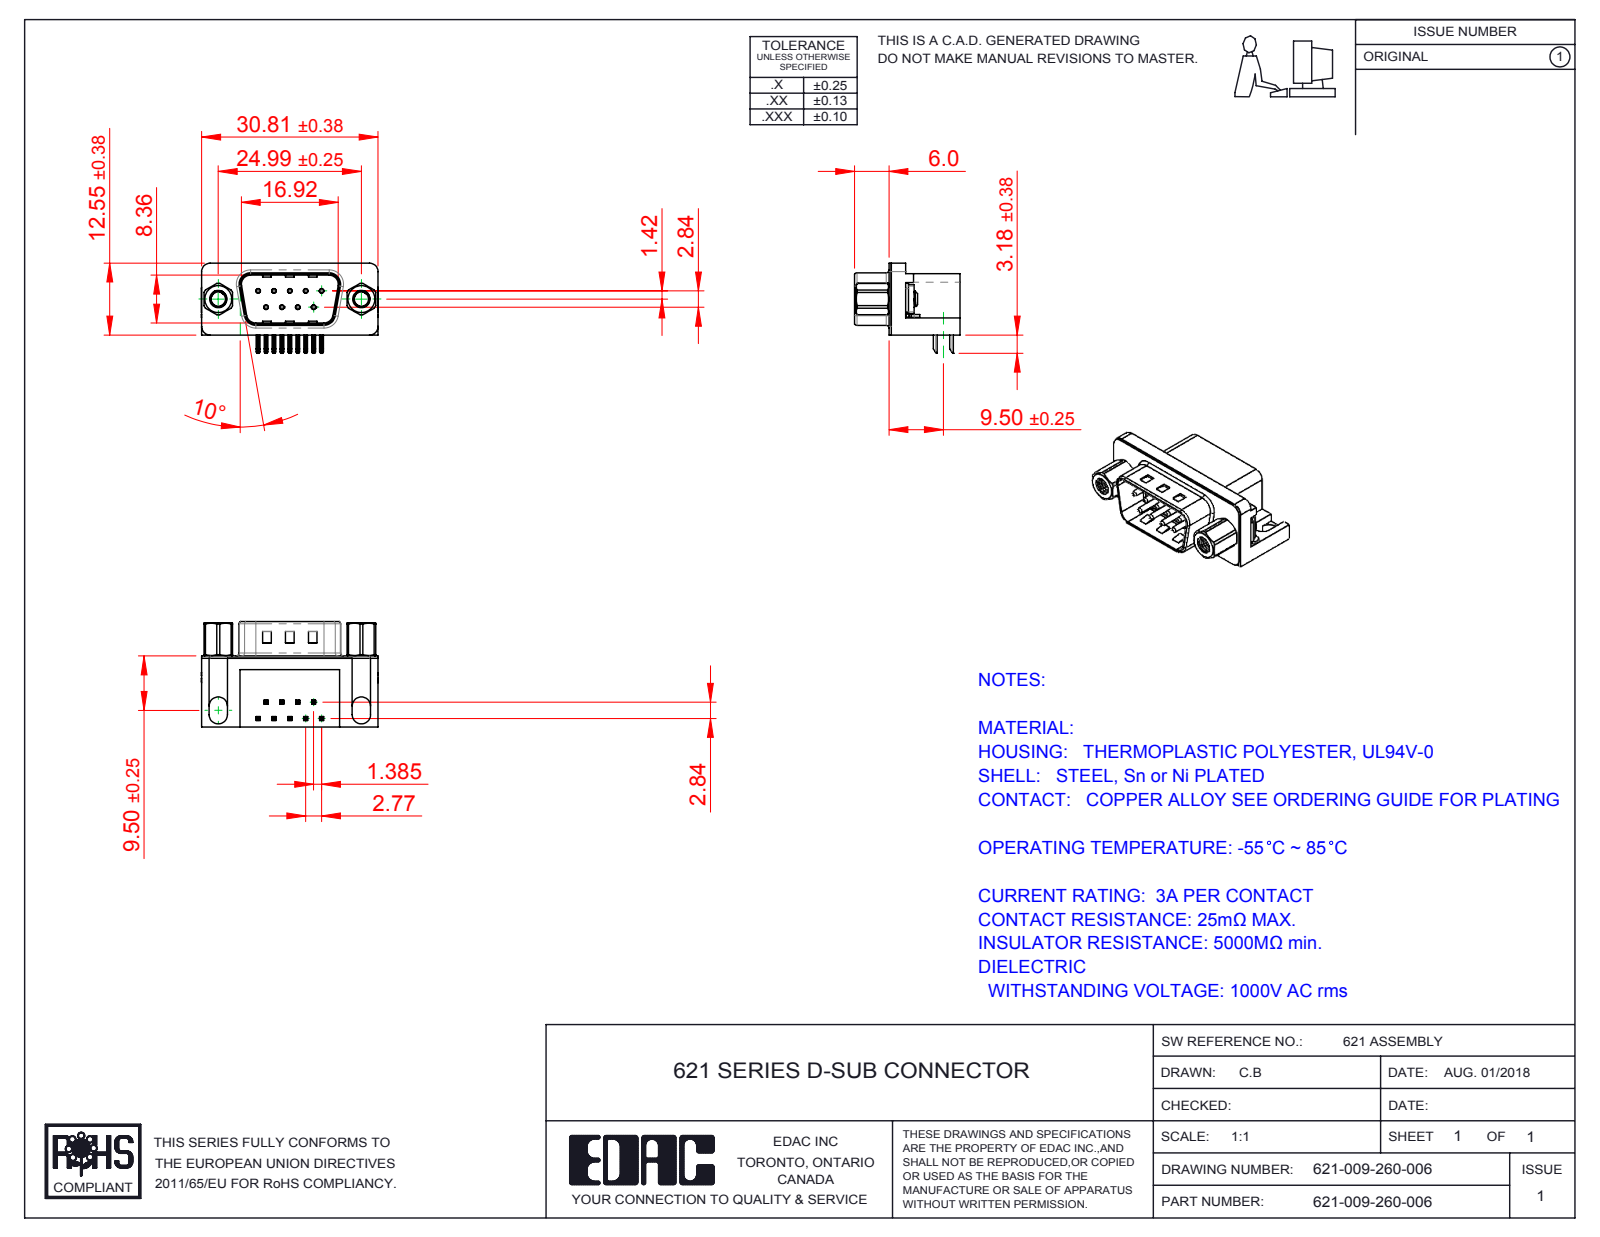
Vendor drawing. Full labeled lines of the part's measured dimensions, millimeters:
Part name (STEP PRODUCT): 621 Non Board Mount; 621 Contact Top; 621 Contact Bottom; 621 Shell_9 Socket (+4 more)
STEP written by: SolidWorks 2016 (CONFIG_CONTROL_DESIGN)
Units: millimetres
Bodies: 17 solids, 1133 faces (593 planar, 407 cylindrical, 133 other)
Overall size (bounding box): 30.89 × 18.4 × 15.73
Volume: 3 449 mm³ · Surface area: 4 780 mm²
Round holes (diameter × count): ⌀0.35 ×9, ⌀0.8 ×9, ⌀2.5 ×2, ⌀4 ×2, ⌀4.8 ×2, ⌀5 ×2
Round bosses / shafts (diameter × count): ⌀0.75 ×9, ⌀4.9 ×2, ⌀4.75 ×2, ⌀3.9 ×2, ⌀3 ×2
Partial cylindrical surfaces — rounded edges, fillets, slot ends (radius × count): R0.25 ×44, R0.12 ×18, R1 ×16, R0.5 ×9, R1.5 ×8, R1.6 ×8, R0.9 ×4, R2 ×4
Main face-to-face distances: 0.4, 12, 12.4, 10.35, 9.5, 2.5, 2.9, 2.1, 0.35, 10.7
Hole centre spacings: 3.16, 2.77, 5.54, 5.03, 5.04, 8.31, 7.48, 7.49
